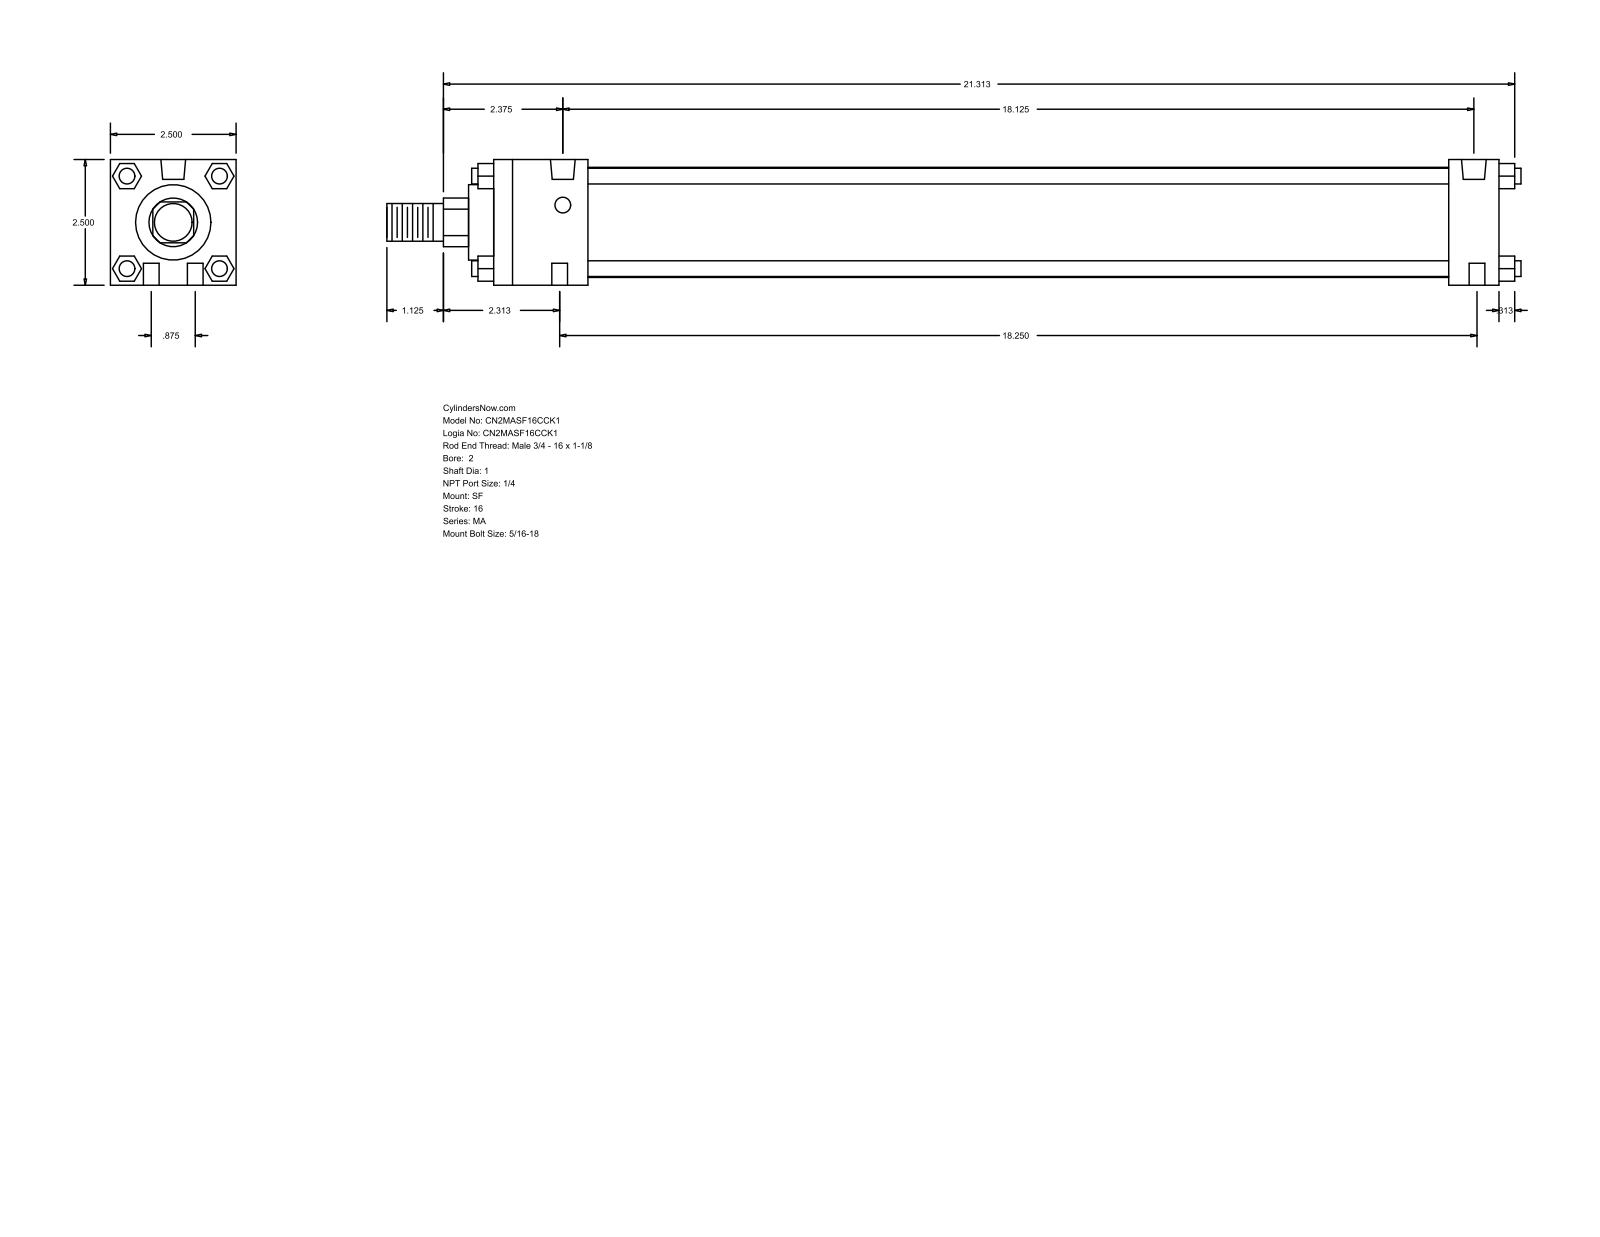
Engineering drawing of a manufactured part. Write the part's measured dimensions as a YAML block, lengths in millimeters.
part_name: "MA_SF__0200_1"
step_written_by: "GSSL Pune (CONFIG_CONTROL_DESIGN)"
units: millimeters
bodies: {solids: 0, faces: 124, planar: 94, cylindrical: 30, other: 0}
overall_size: [573.09, 63.5, 63.5]
round_holes:
  - {diameter: 7.94, count: 6}
  - {diameter: 12.49, count: 2}
round_bosses_or_shafts:
  - {diameter: 7.94, count: 4}
  - {diameter: 55.63, count: 1}
  - {diameter: 38.1, count: 1}
  - {diameter: 25.4, count: 1}
  - {diameter: 19.05, count: 1}
partial_cylinders:
  - {radius: 12.29, count: 1}
face_to_face_distances: [63.5, 508, 12.7, 25.4, 482.6, 47.63, 434.97, 460.37, 40.47, 23.37]
hole_center_spacings: [11.22, 462.09, 22.22, 460.37, 463.55, 464.08]
